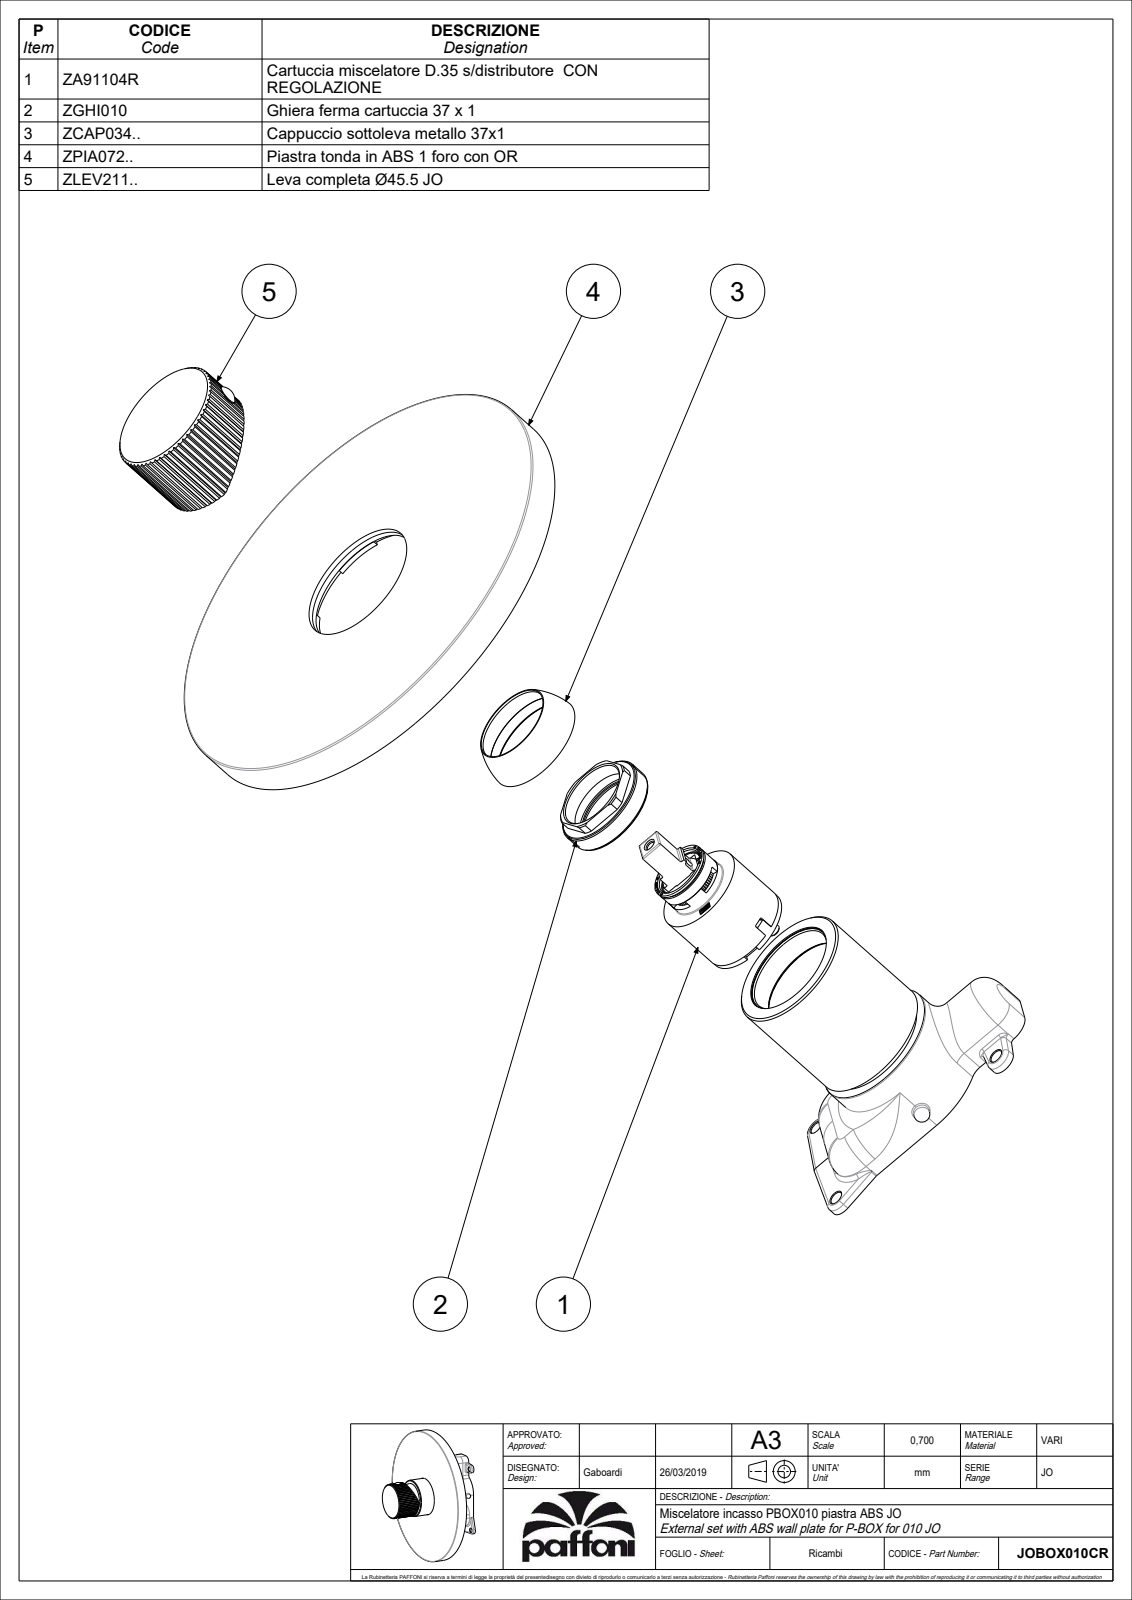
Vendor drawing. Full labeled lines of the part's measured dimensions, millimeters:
Part name (STEP PRODUCT): JOBOX010CR
STEP written by: CREO PARAMETRIC BY PTC INC, 2020044 (CONFIG_CONTROL_DESIGN)
Units: millimetres
Bodies: 1 solid, 263 faces (148 planar, 92 cylindrical, 23 other)
Overall size (bounding box): 173 × 173 × 65.5
Volume: 369 196 mm³ · Surface area: 69 290 mm²
Round holes (diameter × count): ⌀3 ×1, ⌀8 ×1, ⌀42 ×1
Round bosses / shafts (diameter × count): ⌀173 ×1, ⌀48.1 ×1, ⌀16 ×1, ⌀7.6 ×1, ⌀5.5 ×1, ⌀5 ×1
Partial cylindrical surfaces — rounded edges, fillets, slot ends (radius × count): R22.75 ×1
Main face-to-face distances: 13, 62.1, 49.1, 33, 46, 16.1, 31.46, 20, 29.1, 31.47
